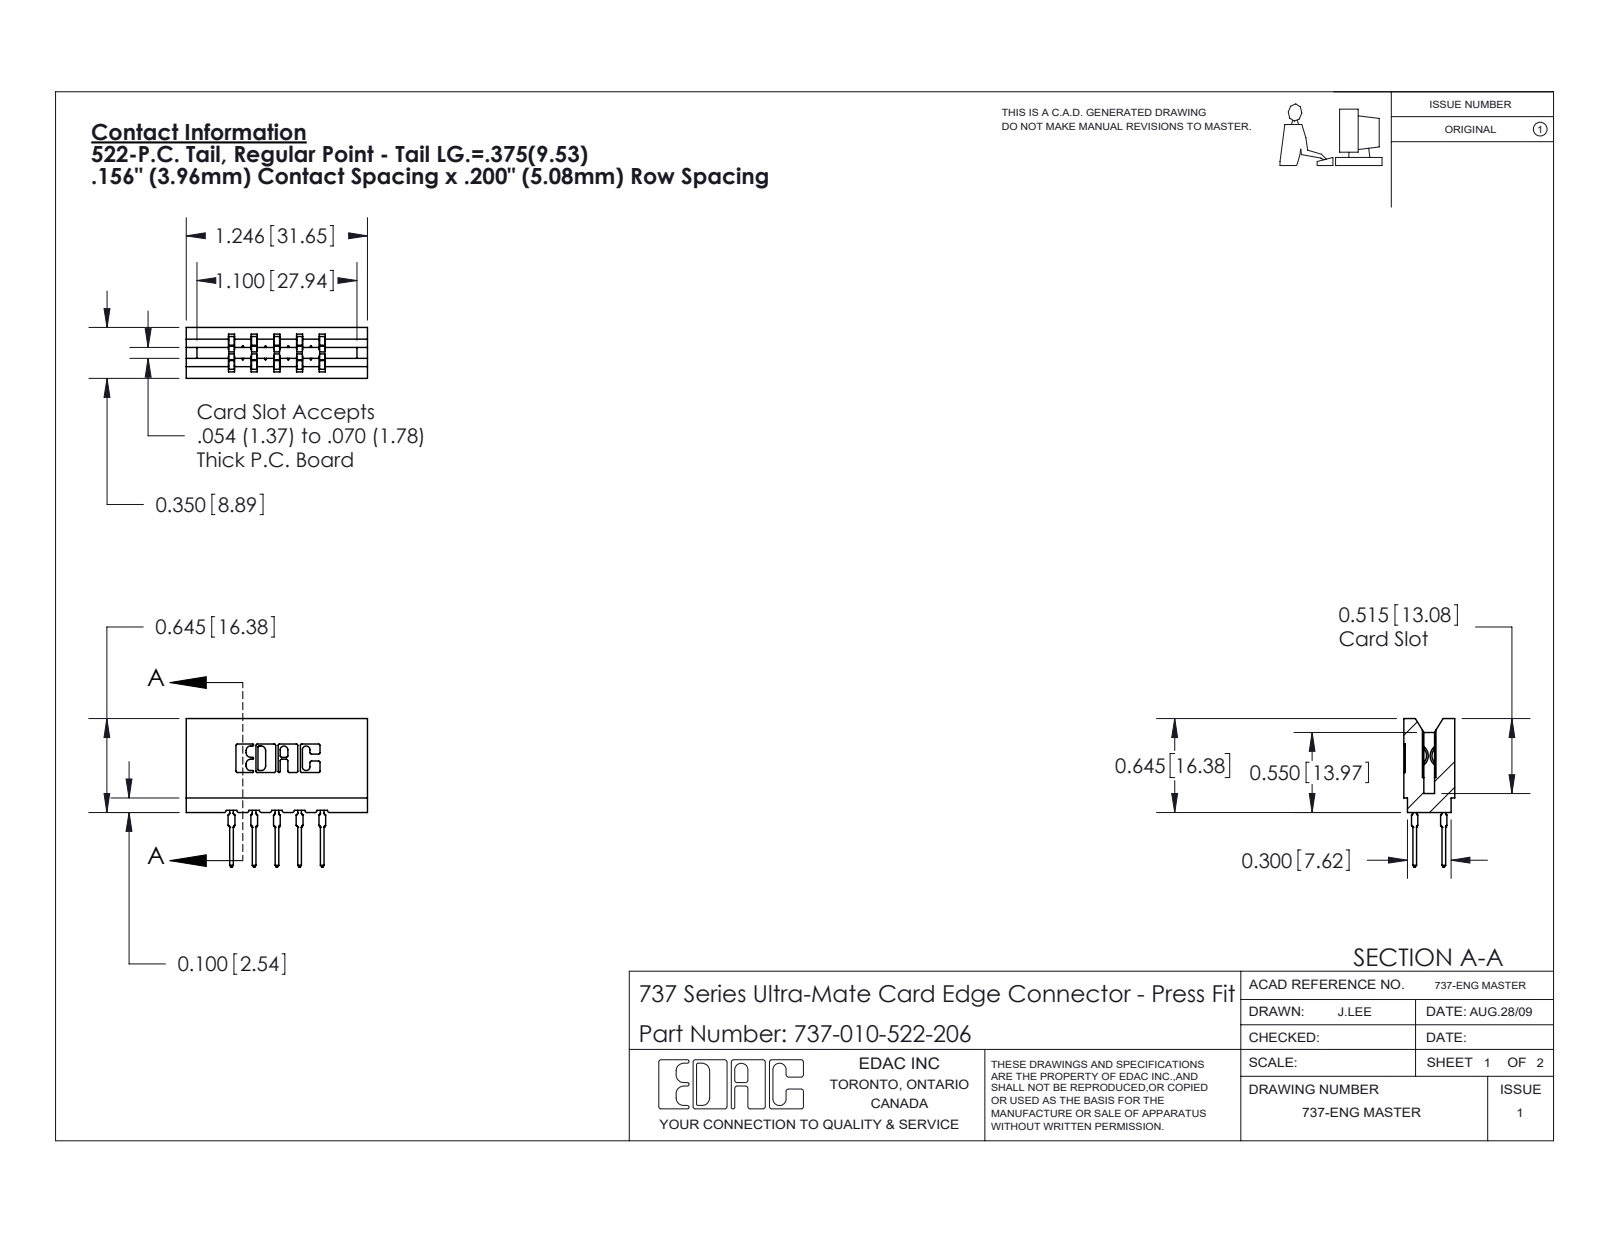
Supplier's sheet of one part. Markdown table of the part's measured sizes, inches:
| quantity | value |
| --- | --- |
| part name | 745-292-001_522; 737 Part_Insulator Option - 06; 737-010-522-206 |
| STEP written by | SolidWorks 2020 (CONFIG_CONTROL_DESIGN) |
| units | inches |
| bodies | 11 solids, 995 faces (520 planar, 215 cylindrical, 260 other) |
| overall size | 1.246 × 1.021 × 0.35 |
| volume | 0.205 in³ |
| surface area | 6.352 in² |
| partial cylindrical surfaces (radius × count) | 0.01 × 22, 0.021 × 20, 0.015 × 10, 0.005 × 8, 0.011 × 8, 0.007 × 6, 0.031 × 6, 0.026 × 3 |
| main face-to-face distances | 0.138, 0.212, 0.156, 0.35, 0.312, 0.198, 0.074, 0.354, 0.042, 0.025 |
